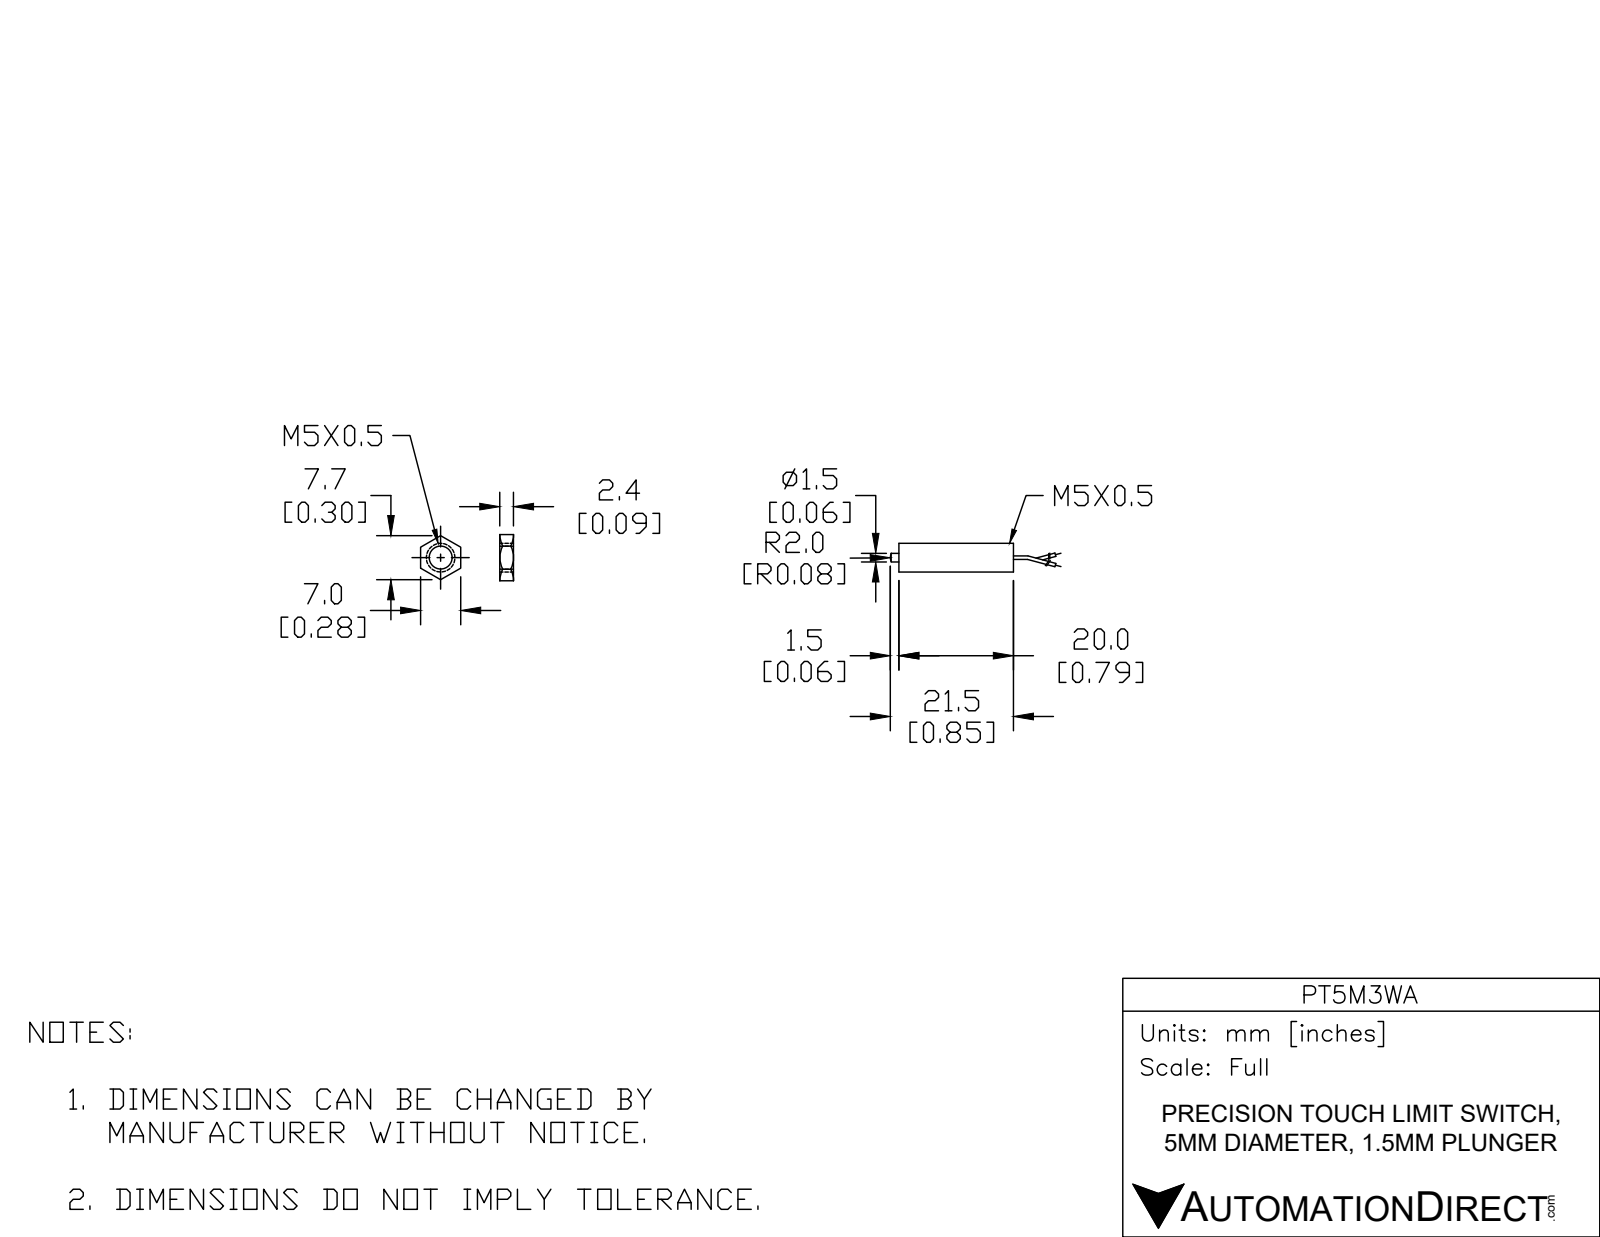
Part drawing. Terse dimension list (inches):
written by: Spatial InterOp 3D (CONFIG_CONTROL_DESIGN)
unit: in
bodies: 1 solid, 97 faces (4 planar, 88 cylindrical, 5 other)
size: 1.24 × 0.197 × 0.197
volume: 0.022 in³; area: 0.915 in²
bosses: 2× ⌀0.024, 1× ⌀0.197, 1× ⌀0.059
face distances: 0.787, 1.181, 0.394
